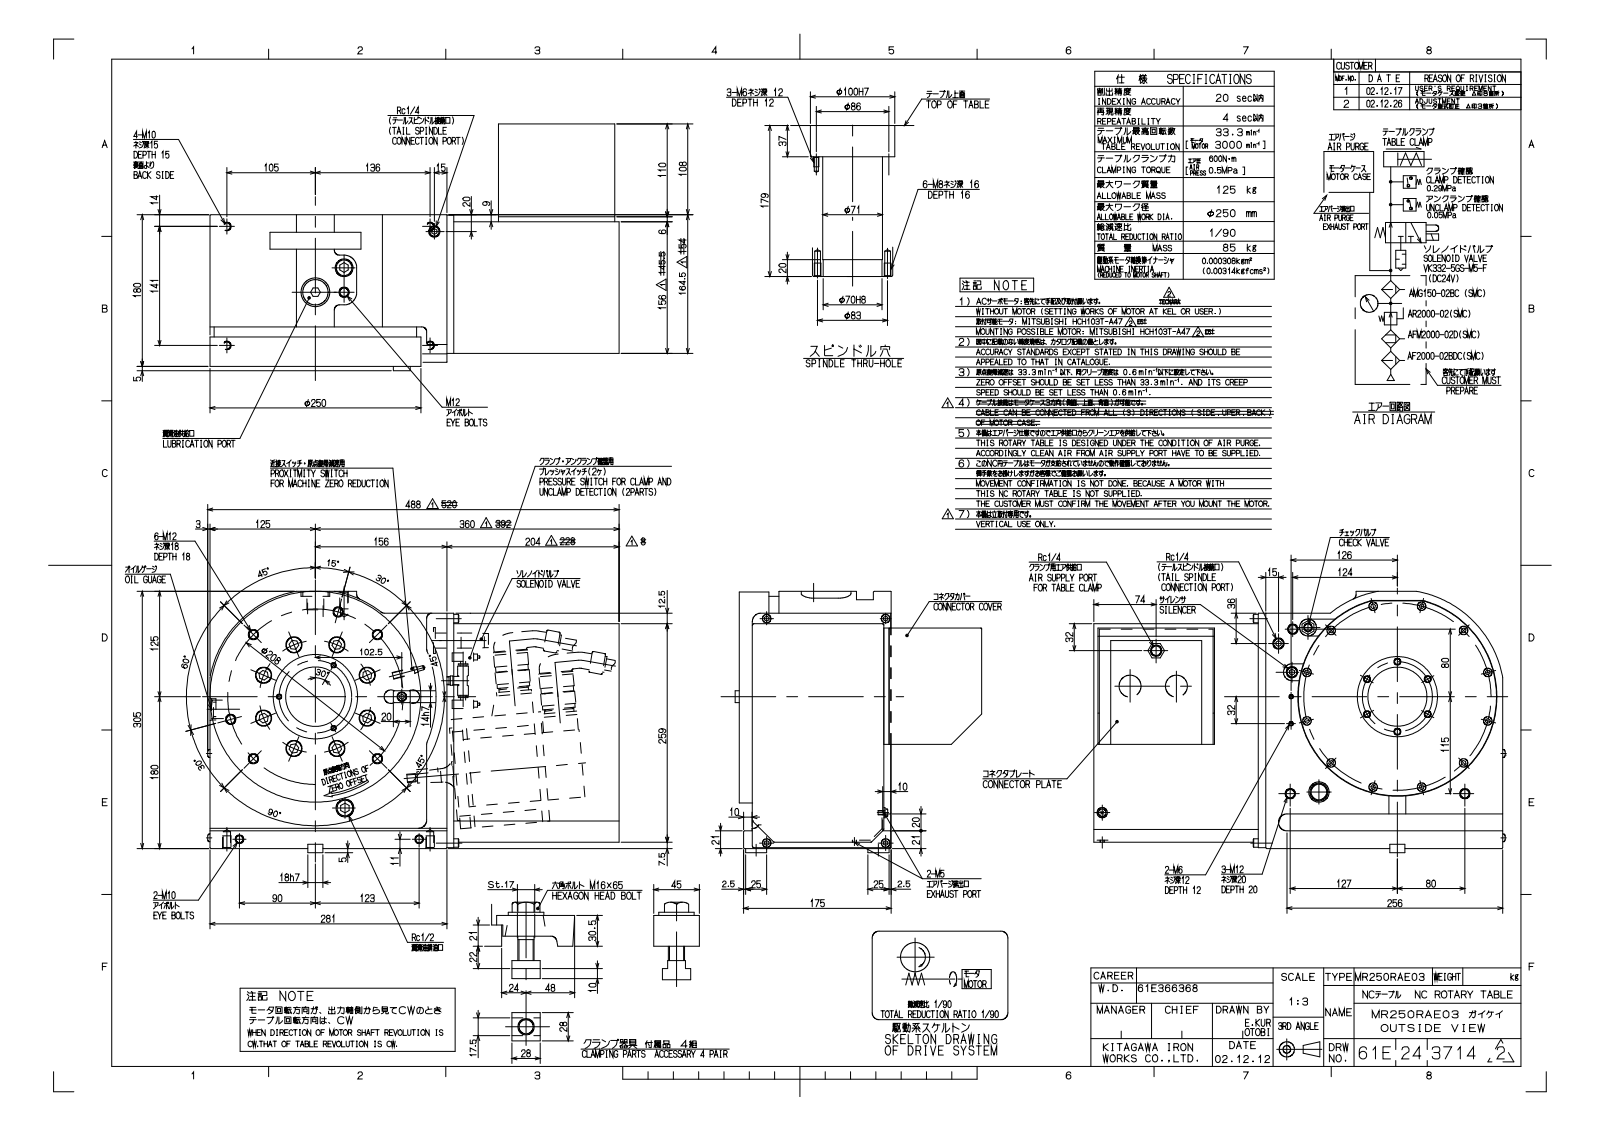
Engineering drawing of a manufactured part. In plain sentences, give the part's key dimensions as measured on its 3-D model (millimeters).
The part is named "MR250RAE03". Its 3-D file was written by "ST-DEVELOPER v16.7 (AUTOMOTIVE_DESIGN)". It is 2 solids with 793 faces: 557 planar, 192 cylindrical and 44 other. Overall it measures 488 by 356.5 by 338 millimeters. Its volume is 12 760 000 cubic millimeters and its surface area 1 158 000 square millimeters. Round holes: 25 of diameter 5, 20 of diameter 10, 15 of diameter 6, 10 of diameter 10.2, 10 of diameter 12, 8 of diameter 8.5, 8 of diameter 19, 6 of diameter 16, 4 of diameter 7, 2 of diameter 13.18, 2 of diameter 20.95, 1 of diameter 9.73. Round bosses or shafts: 4 of diameter 35, 4 of diameter 10, 3 of diameter 9.5, 1 of diameter 250, 1 of diameter 240, 1 of diameter 179, 1 of diameter 99.5, 1 of diameter 30. Partial cylindrical surfaces (rounded edges, fillets, slot ends): 10 of radius 2, 10 of radius 10, 3 of radius 6, 2 of radius 15, 1 of radius 127, 1 of radius 143. The main face-to-face distances are 2.3, 155.7, 2.5, 5.5, 1.6, 256.7, 6.5, 161.2, 163.5, 7.8. The hole center spacings are 45.16, 59, 83.44, 104, 109.02, 64, 141, 118.
